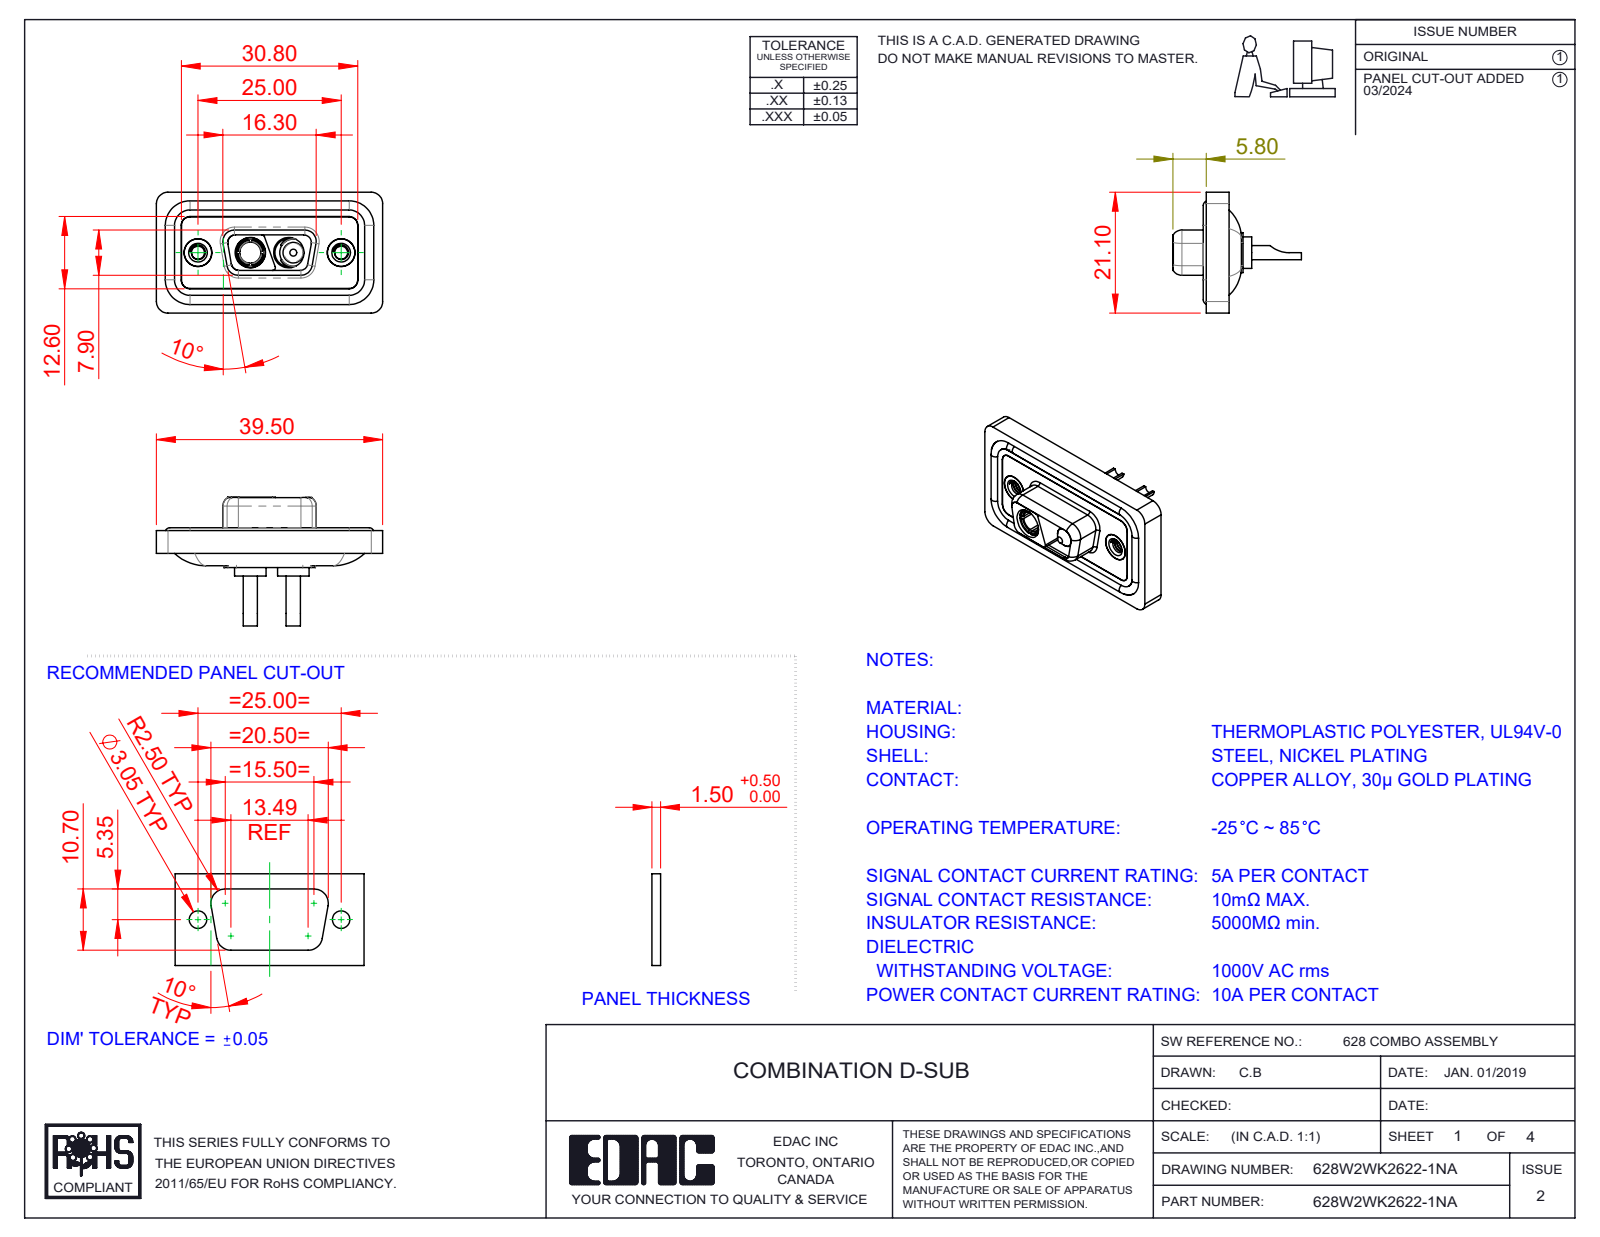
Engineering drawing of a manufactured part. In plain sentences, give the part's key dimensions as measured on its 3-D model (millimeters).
The part is named "Power Pin_10A SC; Power Socket_10A SC; 628Combo Housing_2WK2; 628Combo Shell Front_09 Contacts (+4 more)". Its 3-D file was written by "SolidWorks 2023 (CONFIG_CONTROL_DESIGN)". It is 11 solids with 508 faces: 148 planar, 239 cylindrical and 121 other. Overall it measures 39.5 by 22.45 by 21.1 millimeters. Its volume is 4 599 cubic millimeters and its surface area 7 437 square millimeters. Round holes: 4 of diameter 4.85, 2 of diameter 1.7, 2 of diameter 2.26, 2 of diameter 4, 2 of diameter 4.05, 2 of diameter 5, 2 of diameter 5.3, 1 of diameter 3.7. Round bosses or shafts: 4 of diameter 1.6, 2 of diameter 5.5, 2 of diameter 5.2, 2 of diameter 4.95, 2 of diameter 4.8, 2 of diameter 4.75, 2 of diameter 3.75, 2 of diameter 2.5. Partial cylindrical surfaces (rounded edges, fillets, slot ends): 22 of radius 1.5, 18 of radius 2, 8 of radius 1.35, 8 of radius 1.6, 6 of radius 0.5, 4 of radius 0.25, 4 of radius 0.6, 4 of radius 0.65. The main face-to-face distances are 0.4, 1.1, 2.9, 1.6, 0.5, 1.8, 5.65, 1.5, 5.35, 3.1. The hole center spacings are 9.14, 15.86, 6.72, 25.
